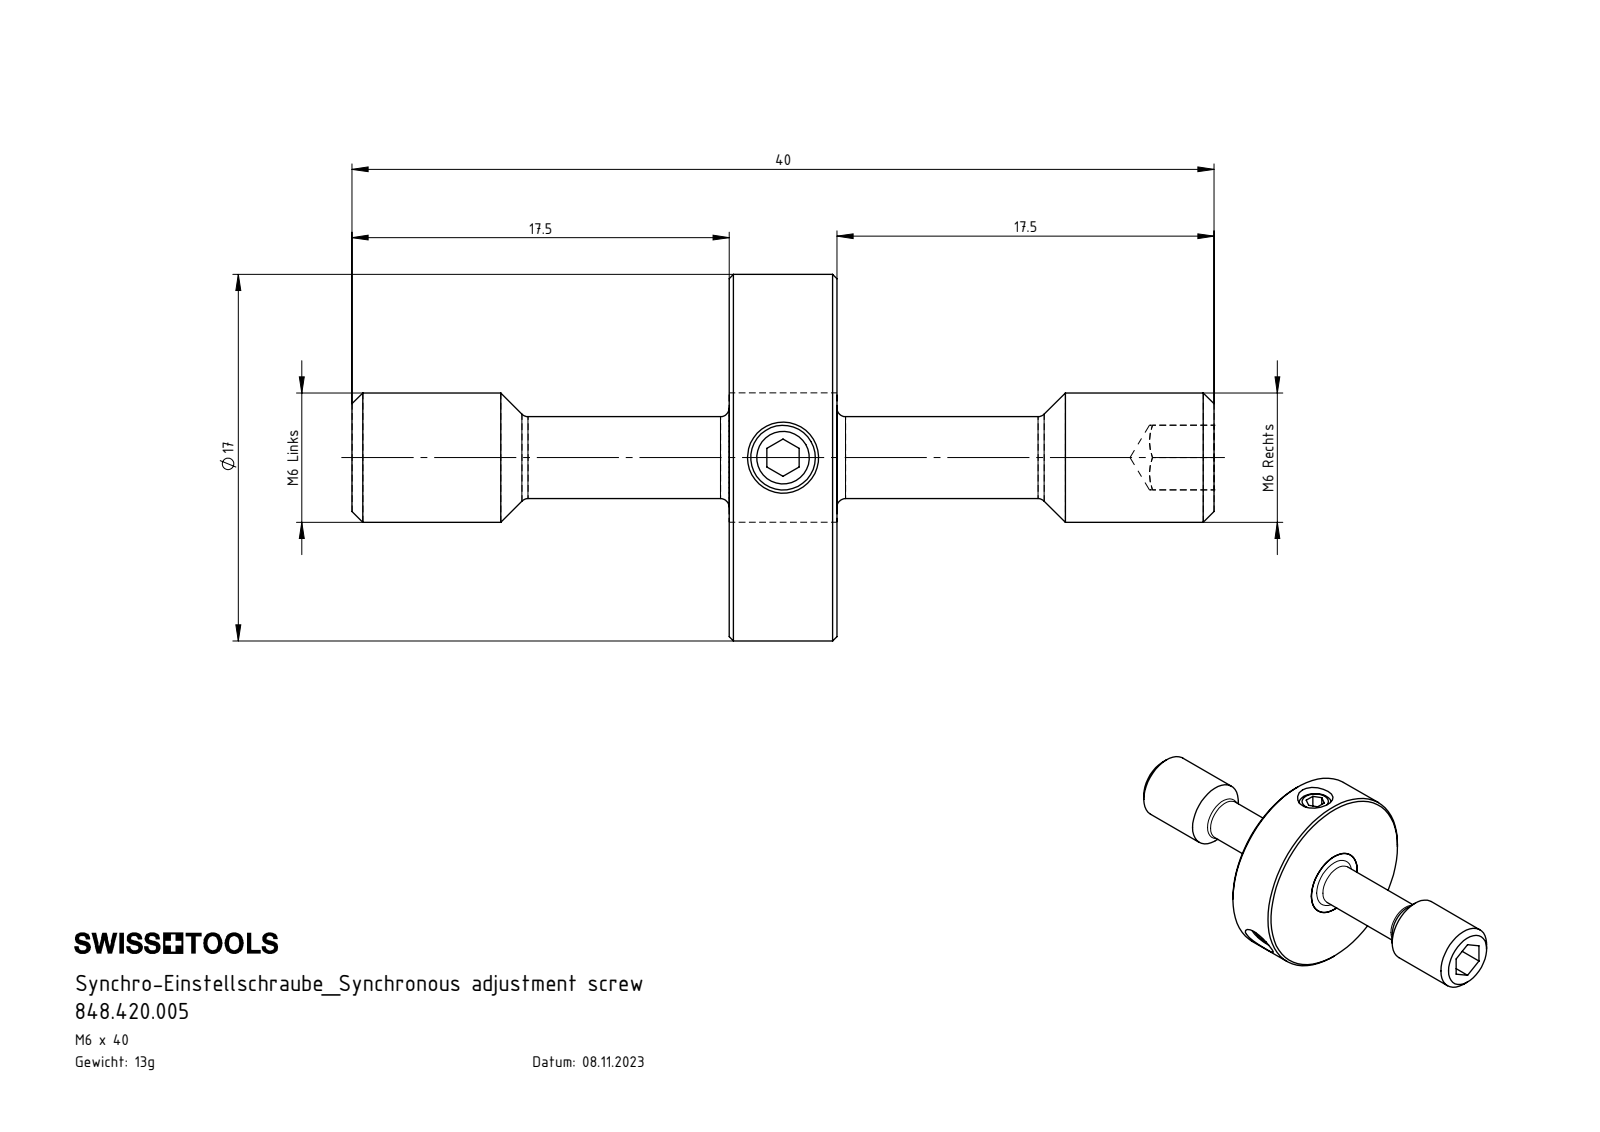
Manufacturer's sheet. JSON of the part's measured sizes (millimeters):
{"part_name": "Z42-ER3.002.005_A; 848.420.005; Z42-ER3.001.040_A; ISO 4026 - M3 x 5", "step_written_by": "SolidWorks 2022 (AUTOMOTIVE_DESIGN)", "units": "millimeters", "bodies": {"solids": 5, "faces": 99, "planar": 39, "cylindrical": 26, "other": 34}, "overall_size": [40, 17, 17], "volume_mm3": 1699, "surface_area_mm2": 1807, "round_holes": [[3.3, 3]], "round_bosses_or_shafts": [[3, 3], [17, 1], [6, 1], [3.8, 1]], "face_to_face_distances": [5, 17.5, 22.5, 3, 1.5, 40, 19.25, 20.75, 1.75, 3.25]}
